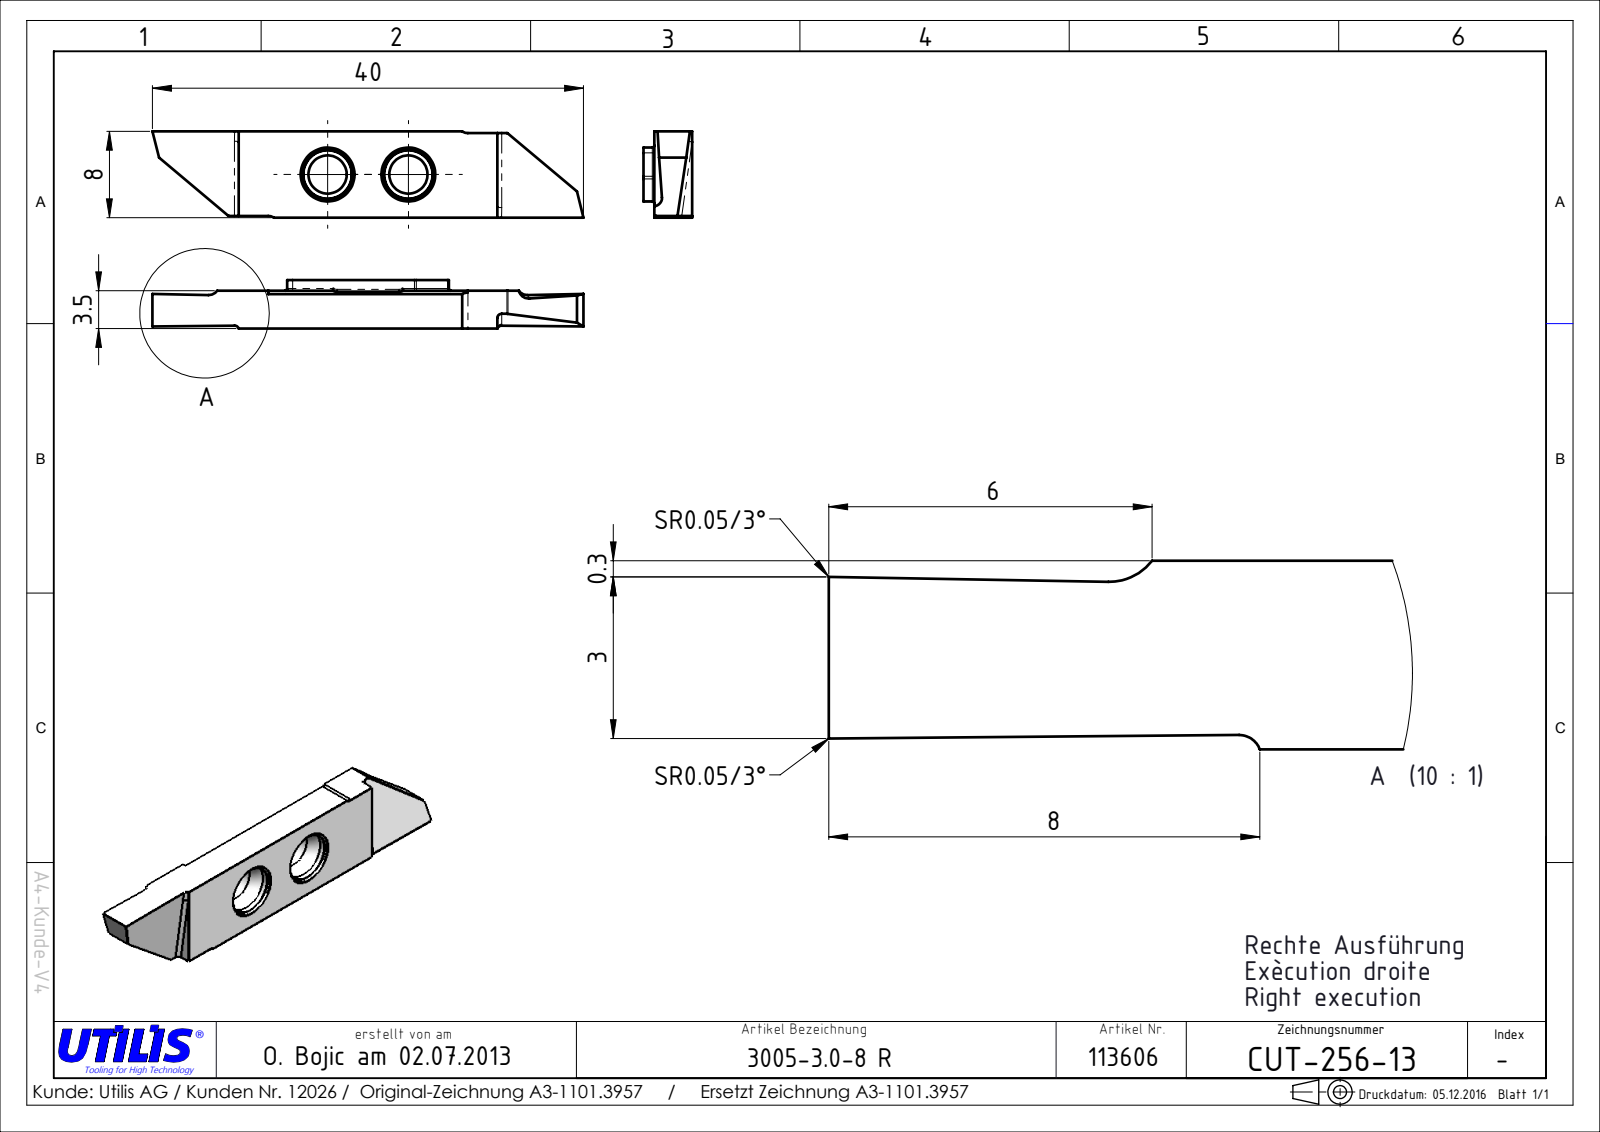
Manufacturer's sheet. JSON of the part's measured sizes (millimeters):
{"part_name": "CUT-256-13", "step_written_by": "SolidWorks 2016 (AUTOMOTIVE_DESIGN)", "units": "millimeters", "bodies": {"solids": 1, "faces": 36, "planar": 22, "cylindrical": 14, "other": 0}, "overall_size": [40, 8, 3.5], "volume_mm3": 853, "surface_area_mm2": 874, "round_holes": [[3.55, 2]], "partial_cylinders_radius": [[0.15, 4], [1, 4], [0.4, 2]], "face_to_face_distances": [3.5, 8, 22.54, 7.85, 7.7, 40, 38.98, 10.75, 29.25, 18.5], "hole_center_spacings": [7.5]}
